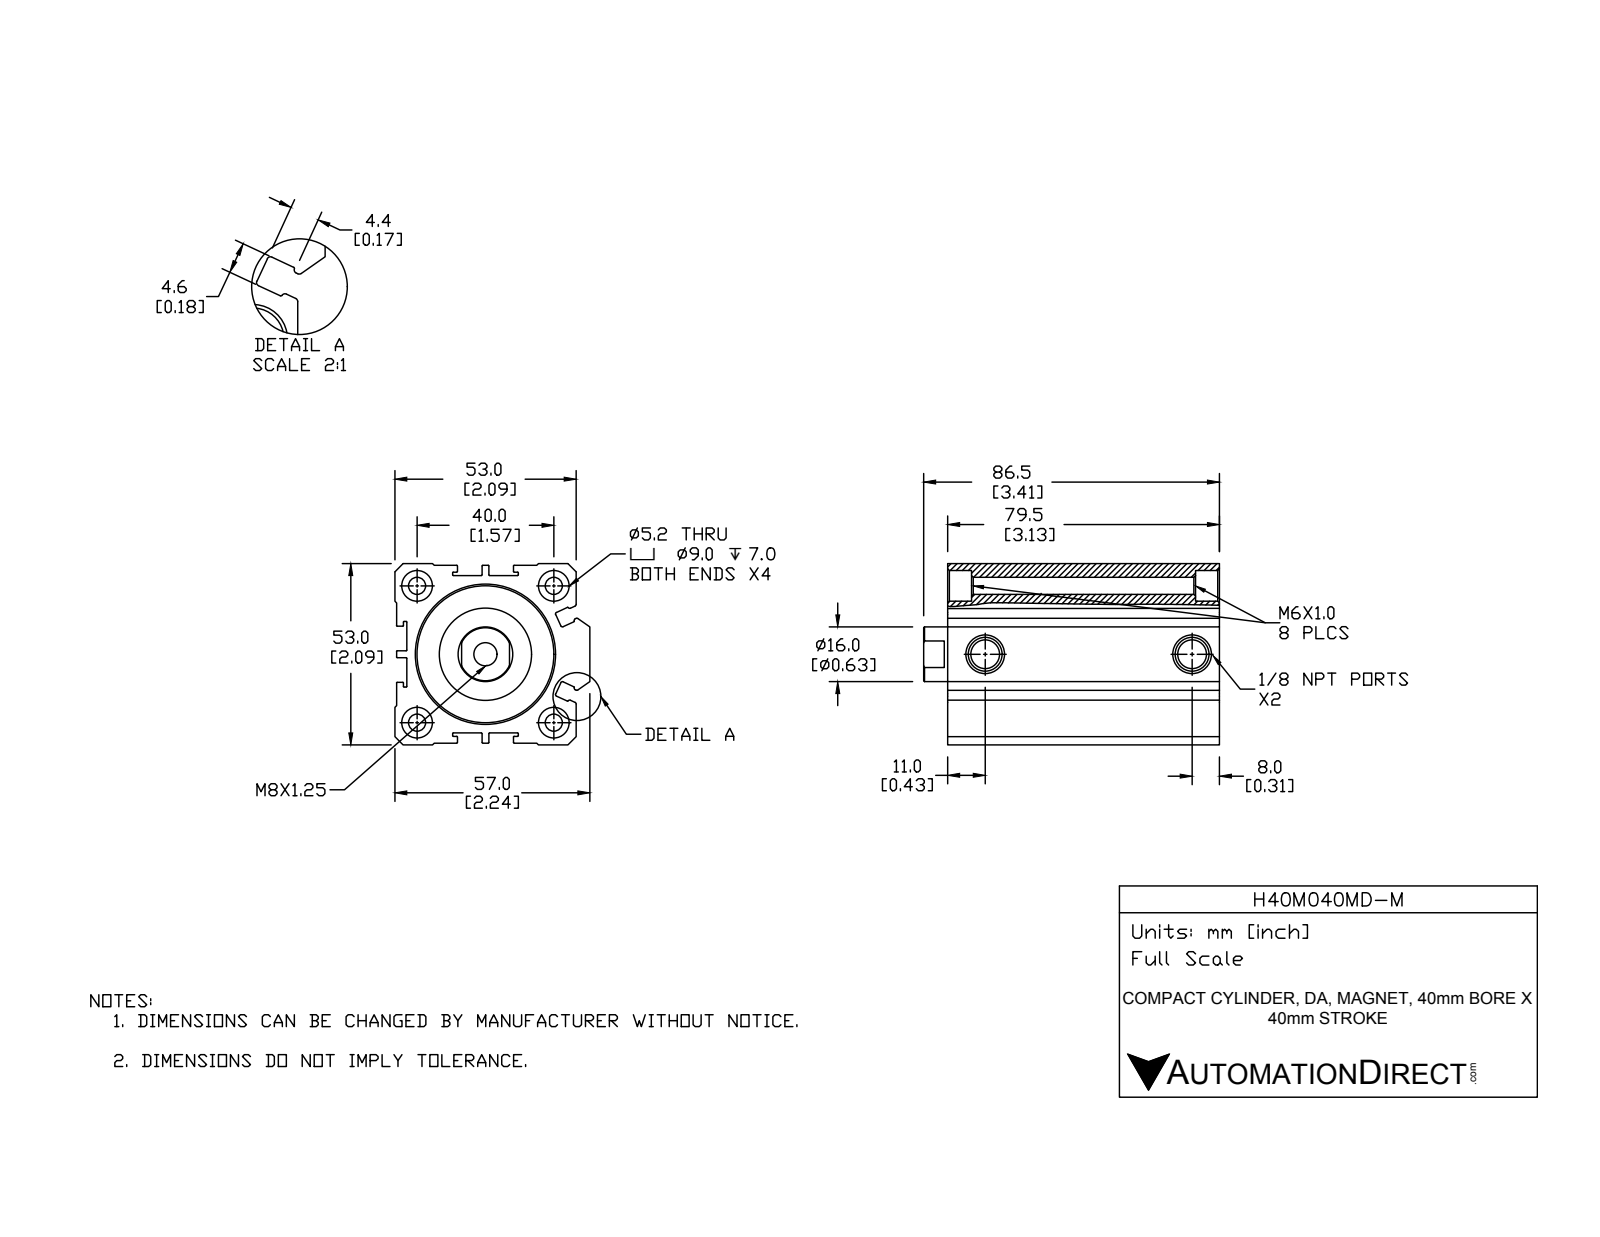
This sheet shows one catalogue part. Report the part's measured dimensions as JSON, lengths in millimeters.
{"part_name": "H40M040MD-M; H40M040MD-M-BODY; H40M040MD-M-PISTON", "step_written_by": "SolidWorks 2015 (CONFIG_CONTROL_DESIGN)", "units": "millimeters", "bodies": {"solids": 2, "faces": 255, "planar": 99, "cylindrical": 103, "other": 53}, "overall_size": [86.5, 57, 53], "volume_mm3": 151696, "surface_area_mm2": 53992, "round_holes": [[5, 4], [9, 4], [8.43, 2], [6.8, 1], [16, 1], [29.5, 1], [40, 1]], "round_bosses_or_shafts": [[27, 1], [25, 1]], "partial_cylinders_radius": [[0.2, 40], [0.5, 12]], "face_to_face_distances": [3.5, 49.5, 0.5, 3, 52.5, 53, 49, 25, 46, 25.5], "hole_center_spacings": [28.28, 40, 56.57, 60.5]}
